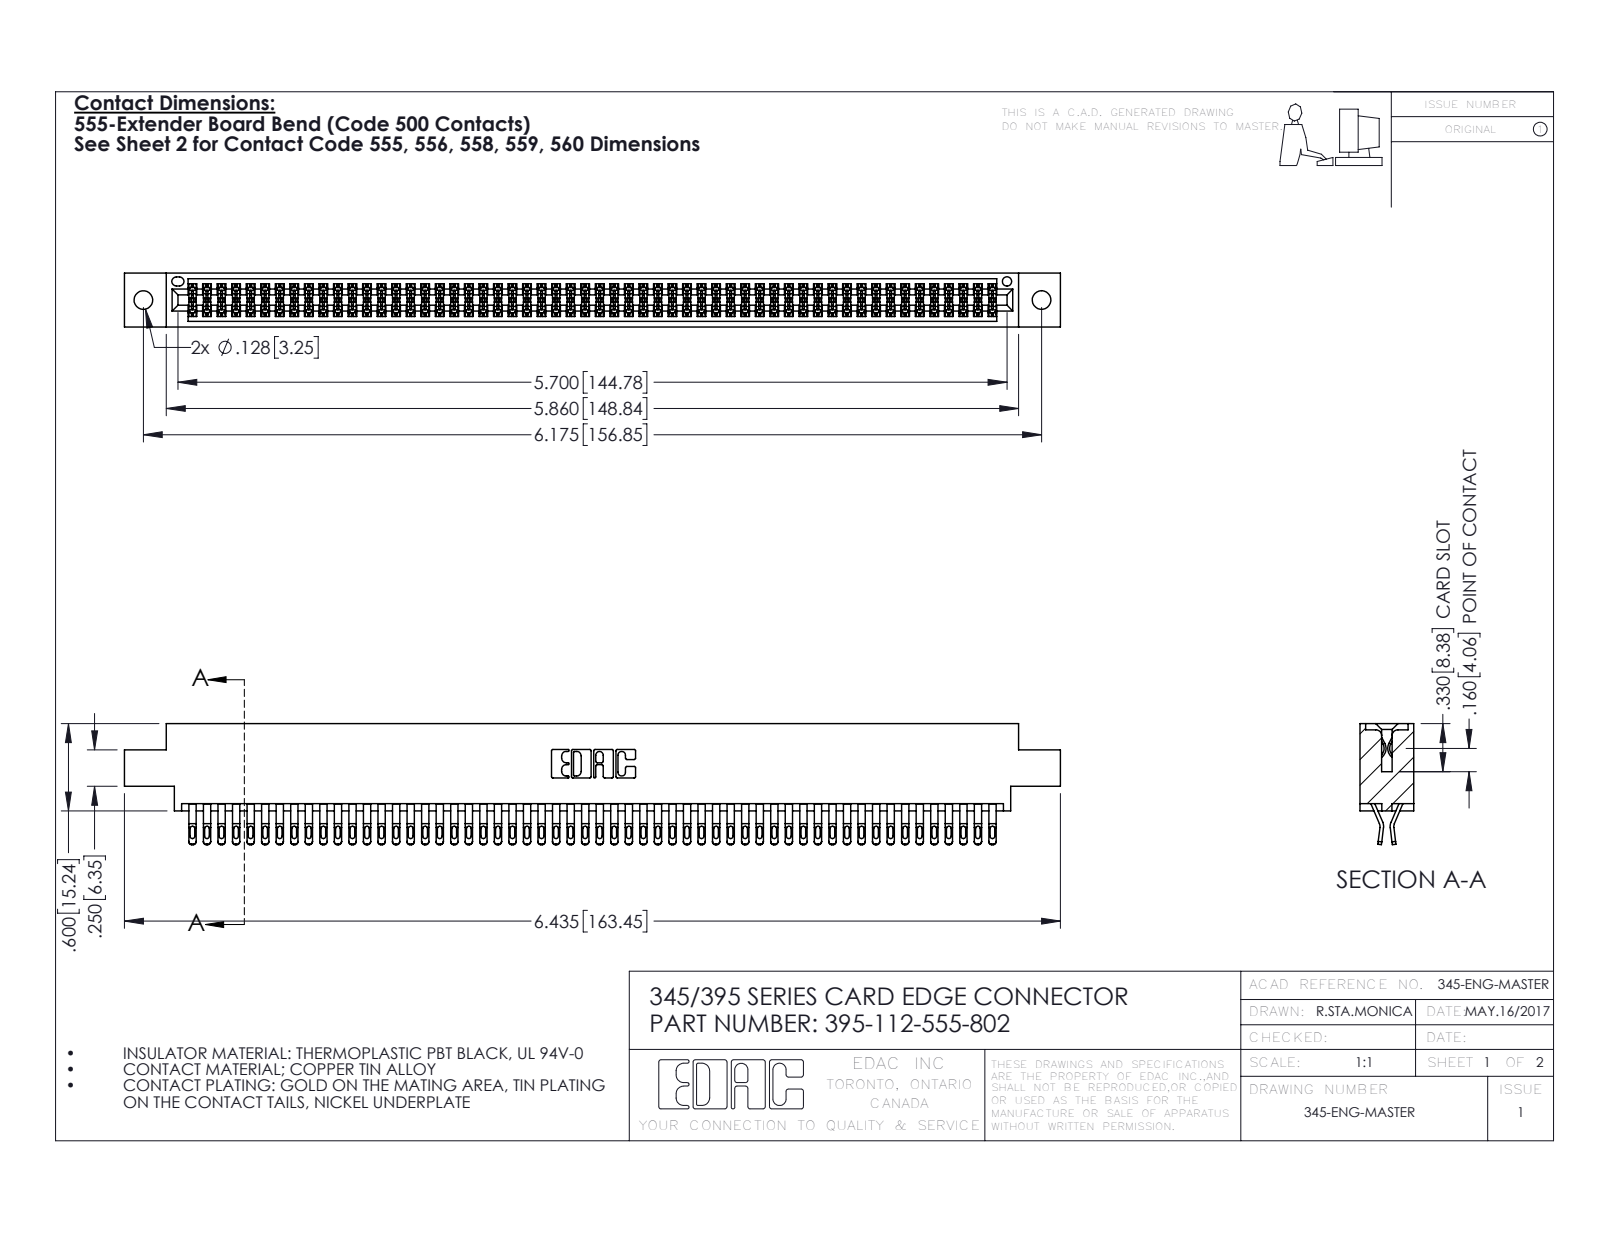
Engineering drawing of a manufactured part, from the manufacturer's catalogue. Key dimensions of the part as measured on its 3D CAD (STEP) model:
Part name (STEP PRODUCT): 345-292-001_555 Tail; 345 Part_0.170 Offset - 0.128 Dia; 395-112-555-802
STEP written by: SolidWorks 2016 (CONFIG_CONTROL_DESIGN)
Units: inches
Bodies: 113 solids, 6402 faces (3556 planar, 2846 cylindrical, 0 other)
Overall size (bounding box): 6.435 × 0.832 × 0.37
Volume: 0.988 in³ · Surface area: 39.05 in²
Round holes (diameter × count): ⌀0.128 ×2, ⌀0.064 ×1
Partial cylindrical surfaces — rounded edges, fillets, slot ends (radius × count): R0.016 ×280, R0.02 ×224, R0.006 ×168, R0.01 ×22, R0.007 ×6, R0.031 ×6, R0.026 ×3, R0.01 ×2
Main face-to-face distances: 0.298, 0.072, 0.37, 0.025, 0.2, 0.098, 0.272, 0.225, 0.175, 0.149
Hole centre spacings: 0.27, 5.939, 6.175
